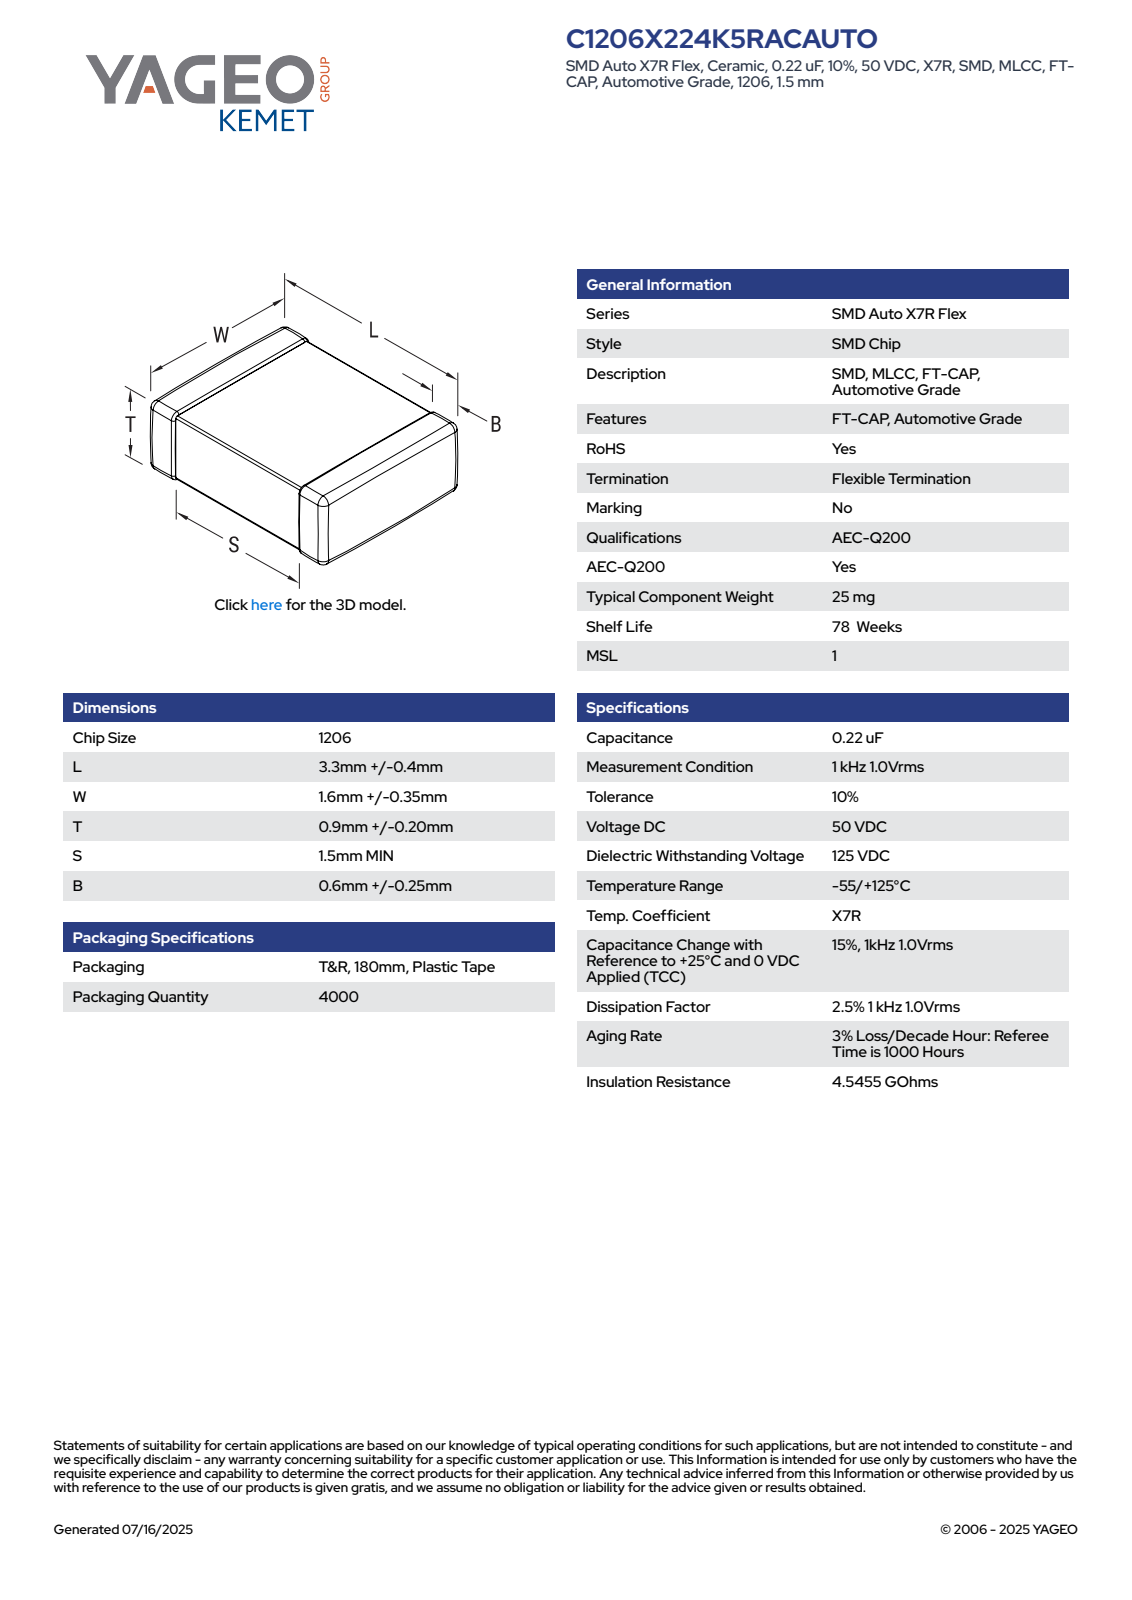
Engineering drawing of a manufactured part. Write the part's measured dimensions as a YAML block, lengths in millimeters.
part_name: "CCS_CCSTD_1206_L3.7W1.95T1.1B0.6"
step_written_by: "SolidWorks 2021 (AUTOMOTIVE_DESIGN)"
units: millimeters
bodies: {solids: 4, faces: 125, planar: 71, cylindrical: 38, other: 16}
overall_size: [3.7, 1.95, 1.1]
volume: 7
surface_area: 27
face_to_face_distances: [1.06, 1.02, 1.91, 1.1, 3.7, 1.87, 1.95, 1.71, 1.99, 2]
